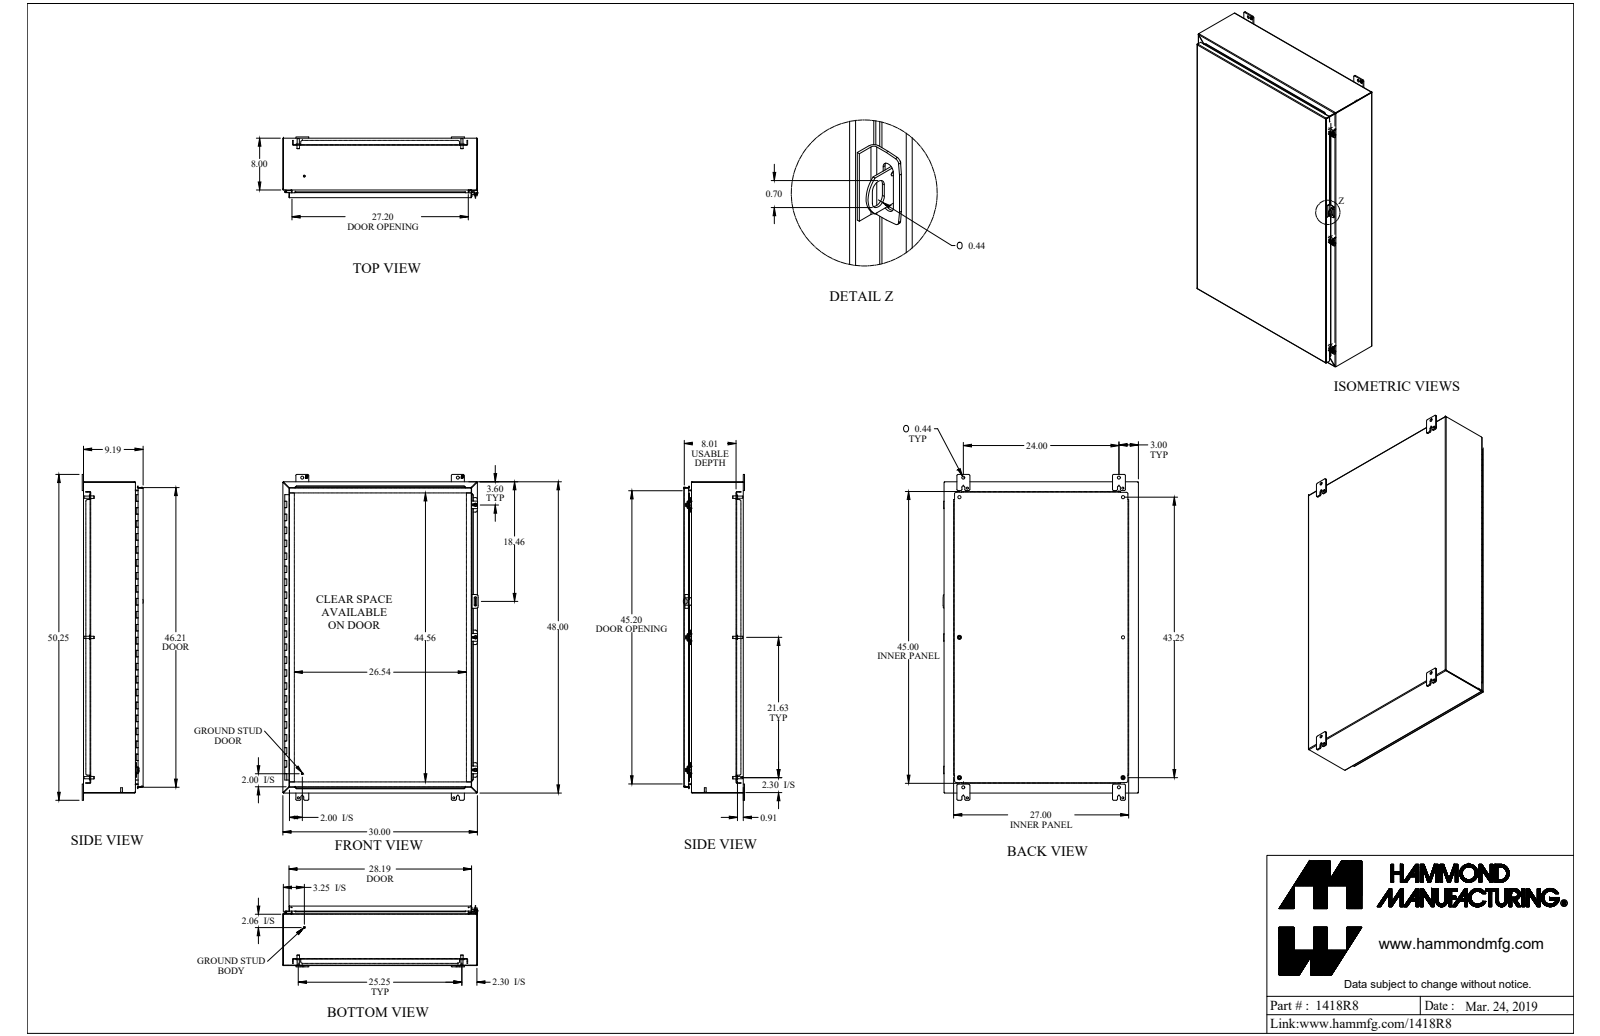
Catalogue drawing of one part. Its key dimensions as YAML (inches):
part_name: "1418R8_Default"
step_written_by: "SolidWorks 2019 (CONFIG_CONTROL_DESIGN)"
units: inches
bodies: {solids: 52, faces: 1710, planar: 995, cylindrical: 621, other: 94}
overall_size: [50.25, 30.125, 9.437]
volume: 507.2
surface_area: 13130
round_holes:
  - {diameter: 0.5, count: 6}
  - {diameter: 0.307, count: 4}
  - {diameter: 0.313, count: 4}
  - {diameter: 0.437, count: 4}
  - {diameter: 0.445, count: 4}
  - {diameter: 0.213, count: 3}
  - {diameter: 0.265, count: 3}
  - {diameter: 0.375, count: 3}
  - {diameter: 0.125, count: 1}
  - {diameter: 0.187, count: 1}
round_bosses_or_shafts:
  - {diameter: 0.65, count: 6}
  - {diameter: 0.375, count: 6}
  - {diameter: 0.33, count: 6}
  - {diameter: 1, count: 4}
  - {diameter: 0.5, count: 3}
  - {diameter: 0.39, count: 3}
  - {diameter: 0.244, count: 3}
  - {diameter: 0.281, count: 2}
partial_cylinders:
  - {radius: 0.188, count: 40}
  - {radius: 0.036, count: 24}
  - {radius: 0.108, count: 24}
  - {radius: 0.25, count: 24}
  - {radius: 0.048, count: 19}
  - {radius: 0.143, count: 19}
  - {radius: 0.116, count: 16}
  - {radius: 0.04, count: 8}
face_to_face_distances: [0.072, 9.113, 9.041, 9.185, 0.937, 0.095, 1.009, 8.081, 8.009, 1.032]
hole_center_spacings: [25.25, 21.625, 21.625, 24, 27.401, 33.244, 33.245, 43.25]
